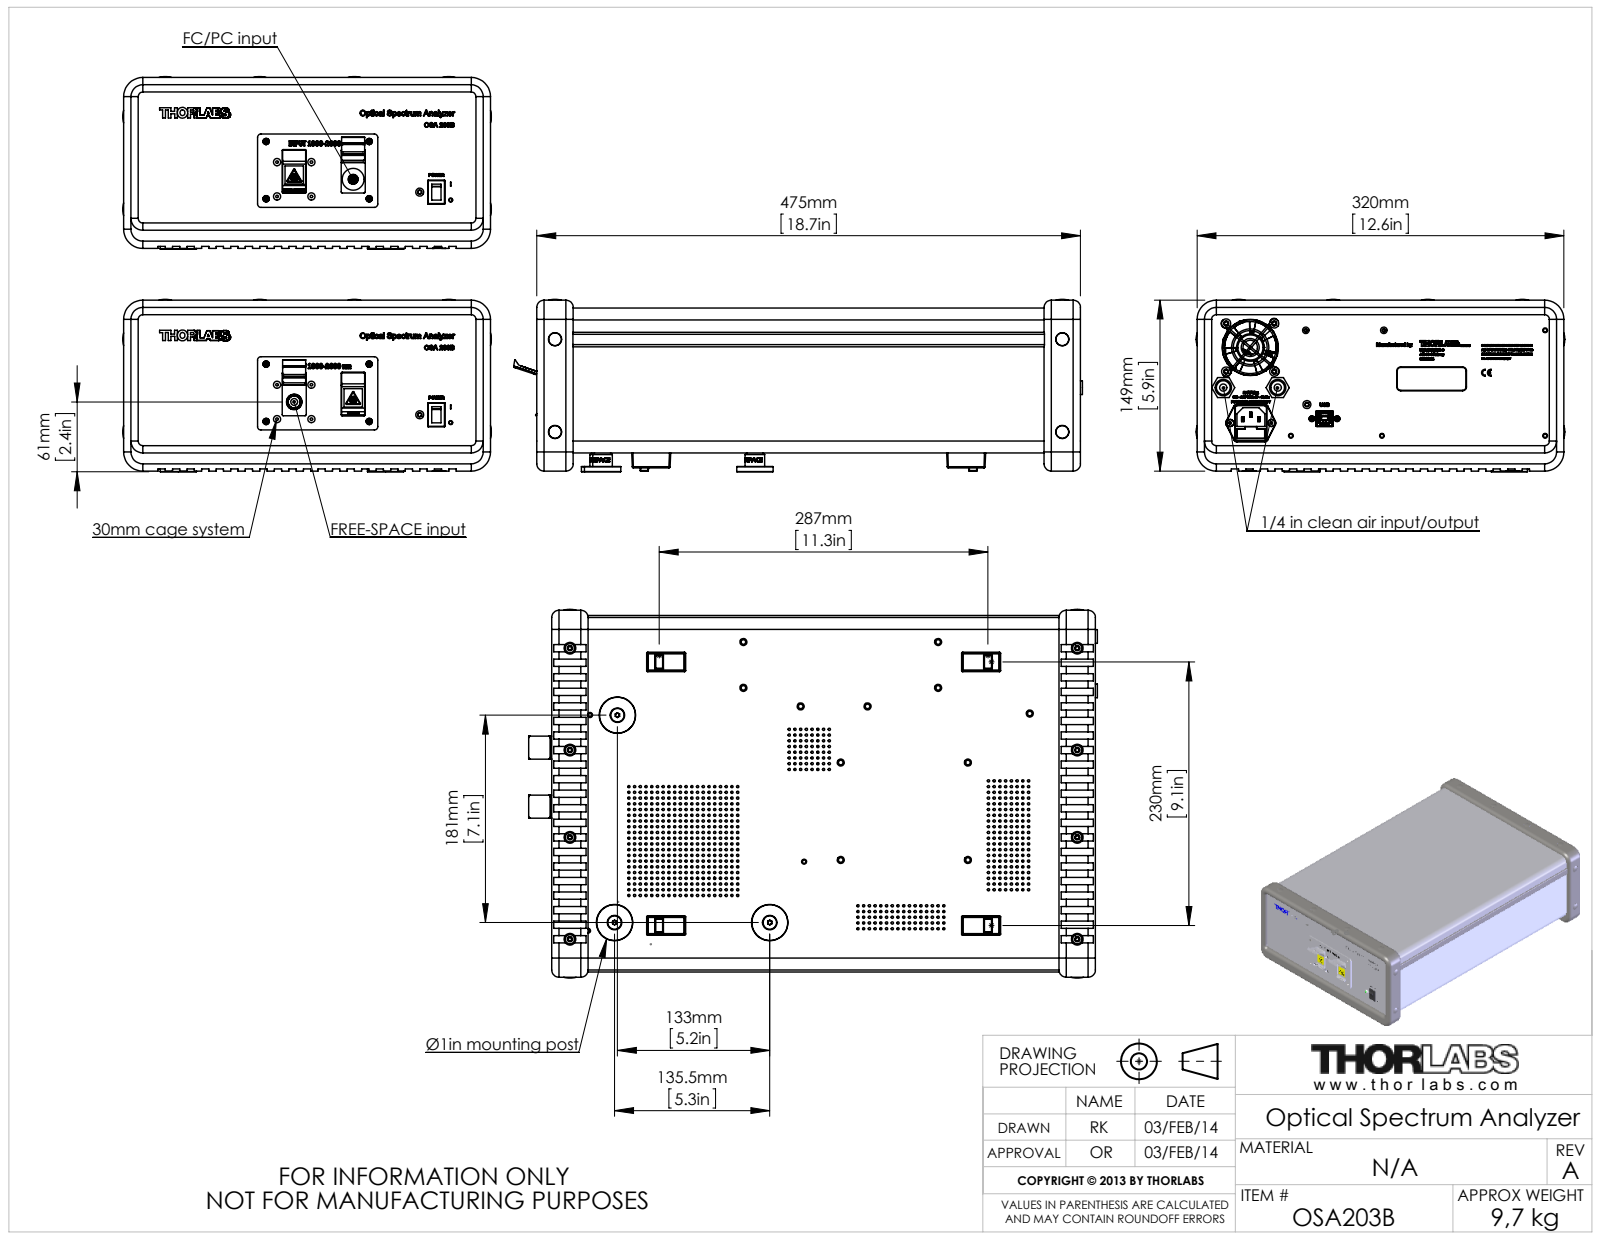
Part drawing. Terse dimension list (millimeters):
name: STN012185-E0W
written by: SolidWorks 2012 (AUTOMOTIVE_DESIGN)
unit: mm
bodies: 0 solids, 2886 faces (804 planar, 1847 cylindrical, 235 other)
size: 496.54 × 321.82 × 150.61
holes: 704× ⌀2, 11× ⌀11.43, 8× ⌀10.16, 4× ⌀6.3, 2× ⌀6.35, 1× ⌀1, 1× ⌀2.26, 1× ⌀2.84, 1× ⌀49
bosses: 12× ⌀11.05, 4× ⌀8, 3× ⌀31.75, 3× ⌀18.4, 3× ⌀17, 3× ⌀3, 3× ⌀1.5, 2× ⌀14.3
rounds: 33× R1, 31× R0.91, 30× R0.5, 18× R6.35, 14× R0.27, 9× R0.38, 6× R1.6, 5× R3
face distances: 1, 125.4, 126.4, 124.4, 306.6, 305.6, 307.6, 3.8, 4.8, 120.6
hole spacings: 5, 10, 30, 15, 20, 25, 35, 40
